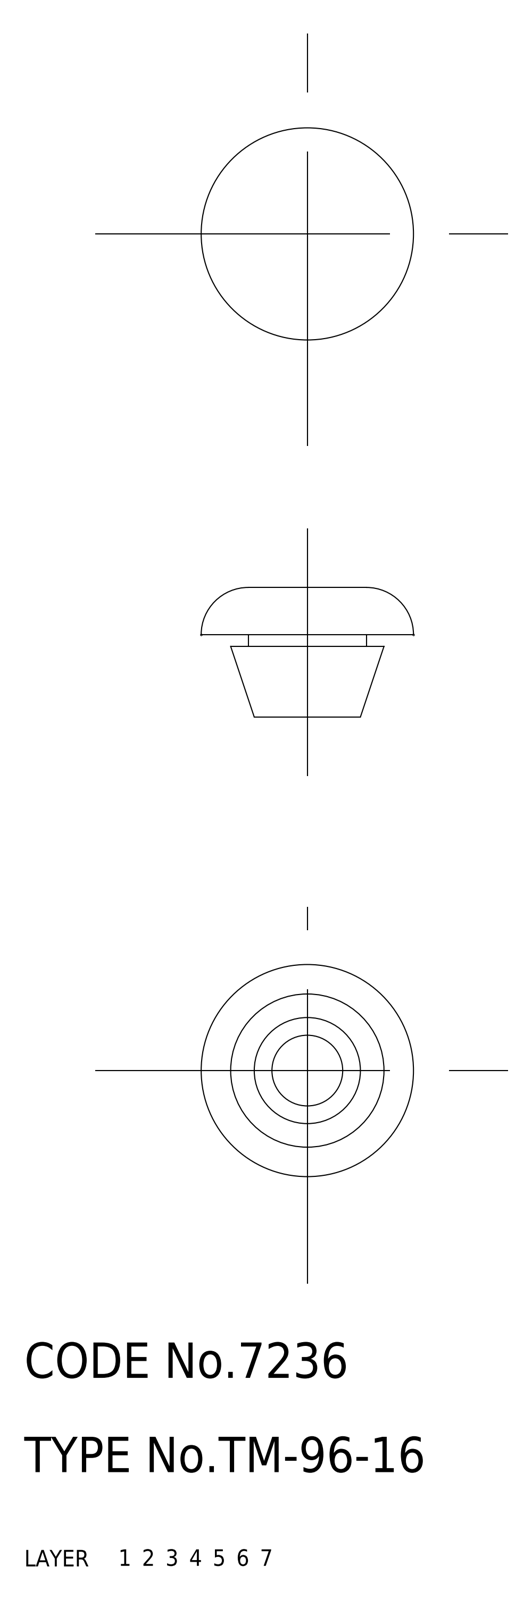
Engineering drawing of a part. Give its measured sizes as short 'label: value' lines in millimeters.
name: cushion
written by: CADfix (AUTOMOTIVE_DESIGN)
unit: mm
bodies: 1 solid, 13 faces (0 planar, 0 cylindrical, 13 other)
size: 18 × 18 × 11
volume: 1 306 mm³; area: 1 052 mm²
